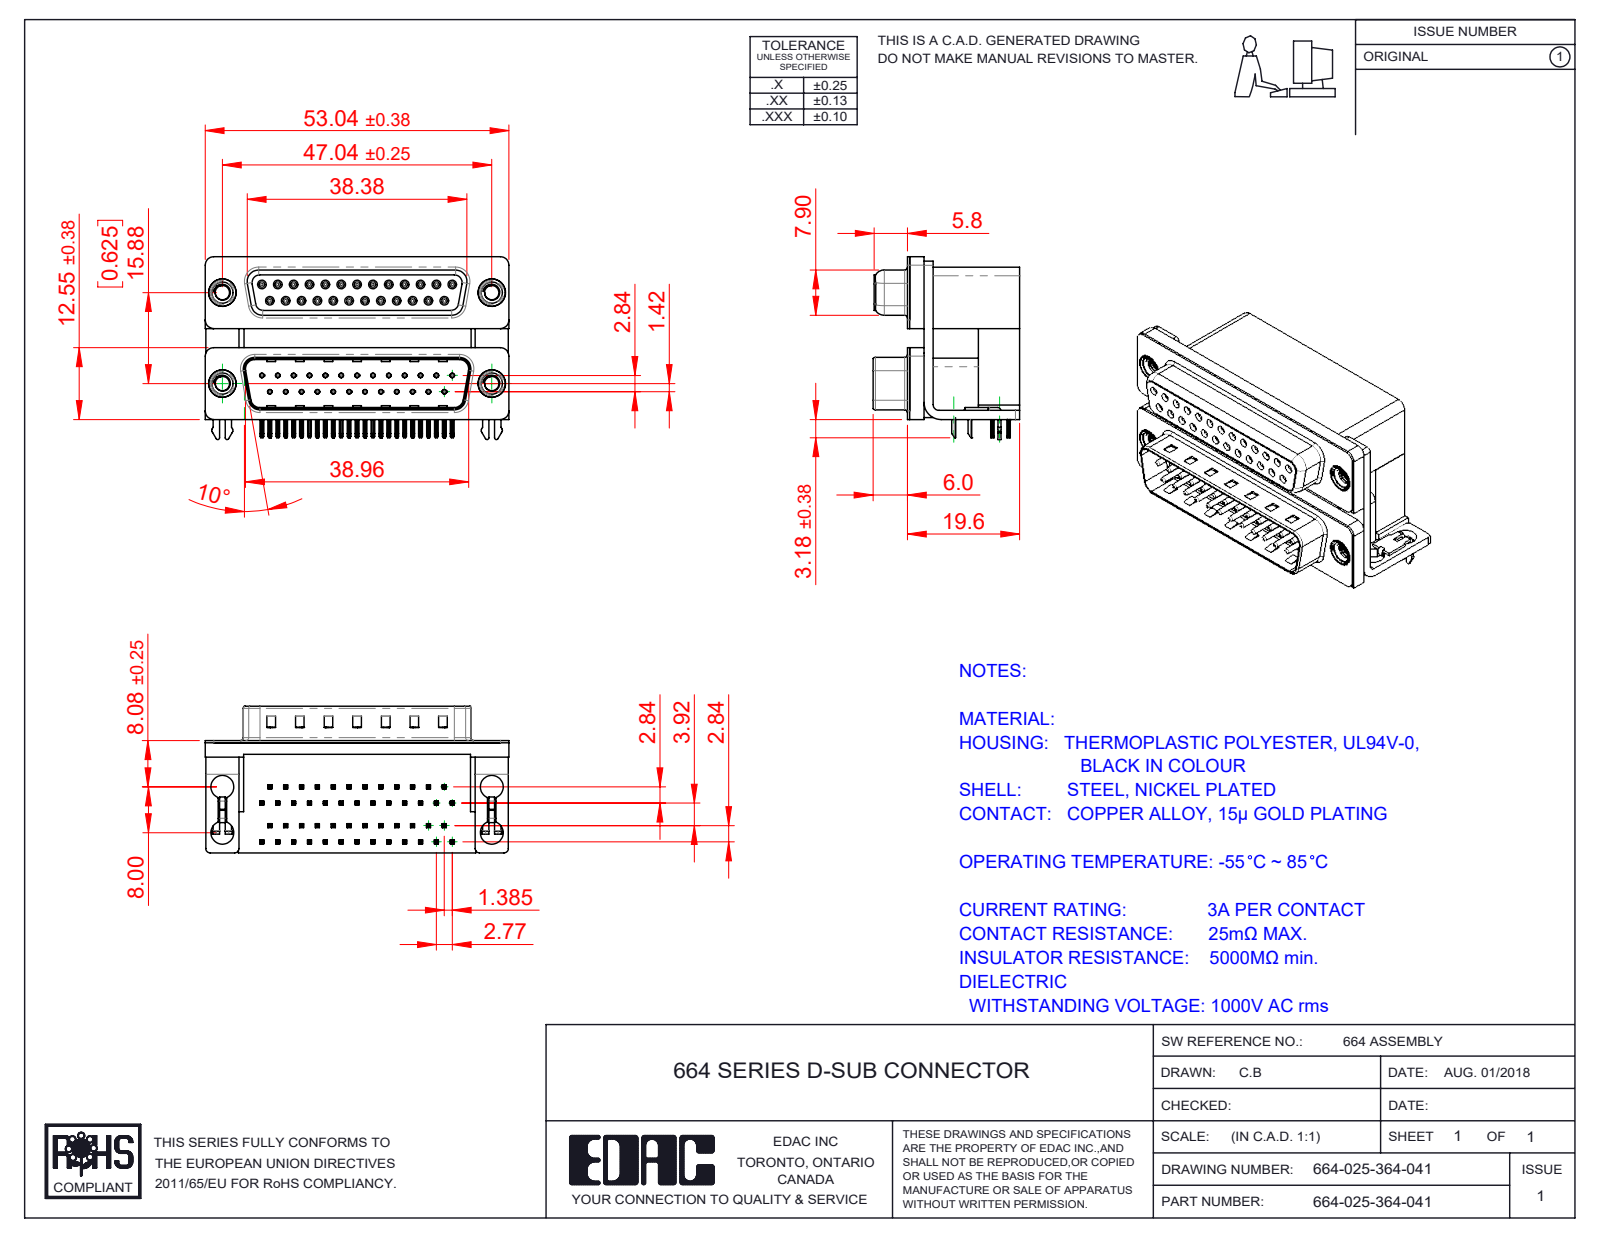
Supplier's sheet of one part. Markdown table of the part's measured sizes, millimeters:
| quantity | value |
| --- | --- |
| part name | 664 Shell Receptacle_25 Contacts; 664 Housing Spacer_25 Contacts L; 664 Contact Top Lower; 664 Housing Lower_25 Contacts (+8 more) |
| STEP written by | SolidWorks 2020 (CONFIG_CONTROL_DESIGN) |
| units | millimeters |
| bodies | 63 solids, 6315 faces (3335 planar, 1581 cylindrical, 1399 other) |
| overall size | 53.04 × 31.93 × 25.6 |
| volume | 21 522 mm³ |
| surface area | 23 362 mm² |
| round holes (diameter × count) | 0.8 × 50, 0.35 × 25, 0.9 × 25, 4 × 8, 2.5 × 4, 3.5 × 4, 4.8 × 4, 5 × 4 |
| round bosses / shafts (diameter × count) | 1.2 × 25, 0.75 × 25, 4.9 × 4, 4.75 × 4, 3.9 × 4 |
| partial cylindrical surfaces (radius × count) | 0.1 × 201, 0.25 × 106, 0.15 × 100, 0.12 × 50, 0.35 × 50, 0.34 × 25, 0.5 × 16, 1.5 × 13 |
| main face-to-face distances | 0.4, 19.2, 7.2, 12, 10.7, 16.7, 9.5, 2.5, 15.53, 26.23 |
| hole center spacings | 2.77, 3.16, 5.54, 8.31, 11.08, 13.85, 16.62, 5.03 |
